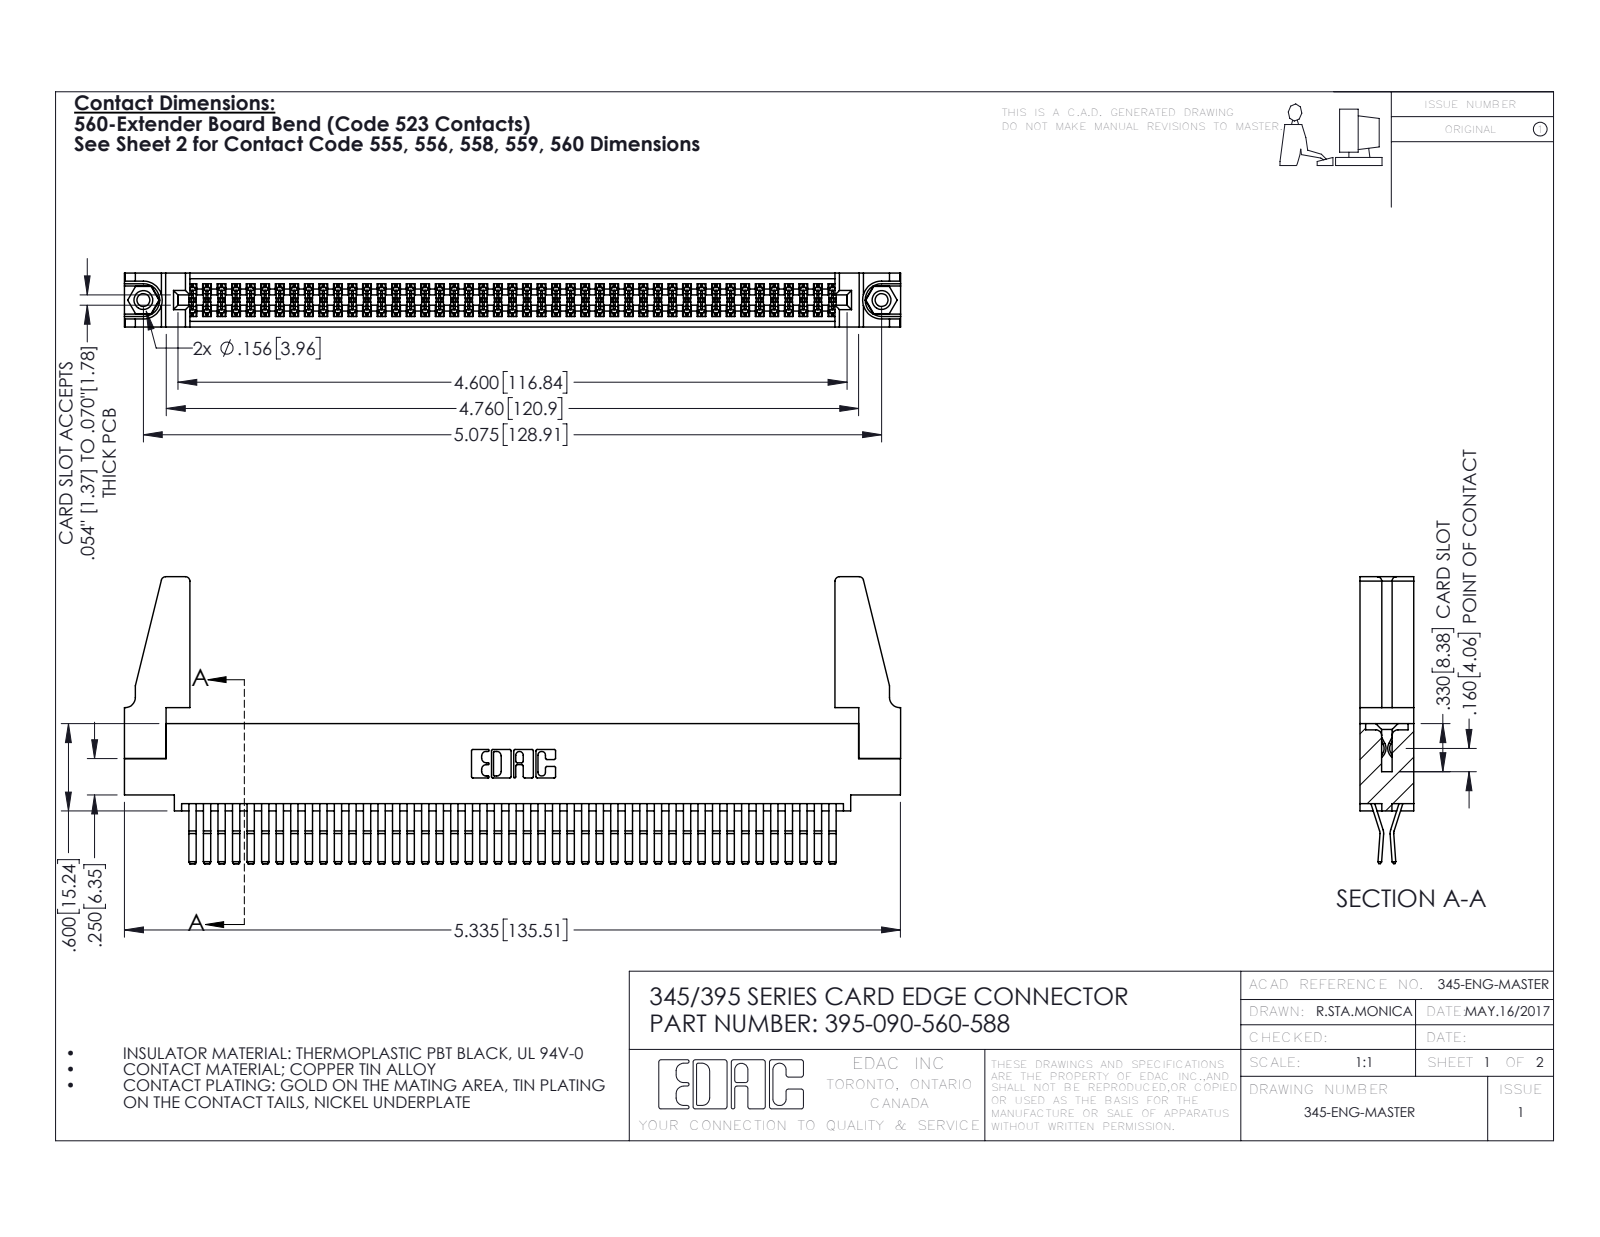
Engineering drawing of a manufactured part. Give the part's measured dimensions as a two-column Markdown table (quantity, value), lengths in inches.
| quantity | value |
| --- | --- |
| part name | 345-250-001_345-250-001-102; 395-090-560-588; 345-220-078_345-220-088; 345-292-001_560 Tail (+1 more) |
| STEP written by | SolidWorks 2016 (CONFIG_CONTROL_DESIGN) |
| units | inches |
| bodies | 95 solids, 4934 faces (3126 planar, 1792 cylindrical, 16 other) |
| overall size | 5.336 × 1.972 × 0.37 |
| volume | 1.035 in³ |
| surface area | 38.84 in² |
| round holes (diameter × count) | 0.089 × 2, 0.125 × 2, 0.156 × 2, 0.064 × 1 |
| round bosses / shafts (diameter × count) | 0.155 × 2 |
| partial cylindrical surfaces (radius × count) | 0.006 × 135, 0.01 × 22, 0.03 × 8, 0.007 × 6, 0.031 × 6, 0.026 × 3, 0.01 × 2, 0.014 × 2 |
| main face-to-face distances | 0.072, 0.298, 0.025, 0.37, 0.2, 0.098, 0.272, 0.225, 0.175, 0.149 |
| hole center spacings | 0.27, 4.839, 5.075 |
